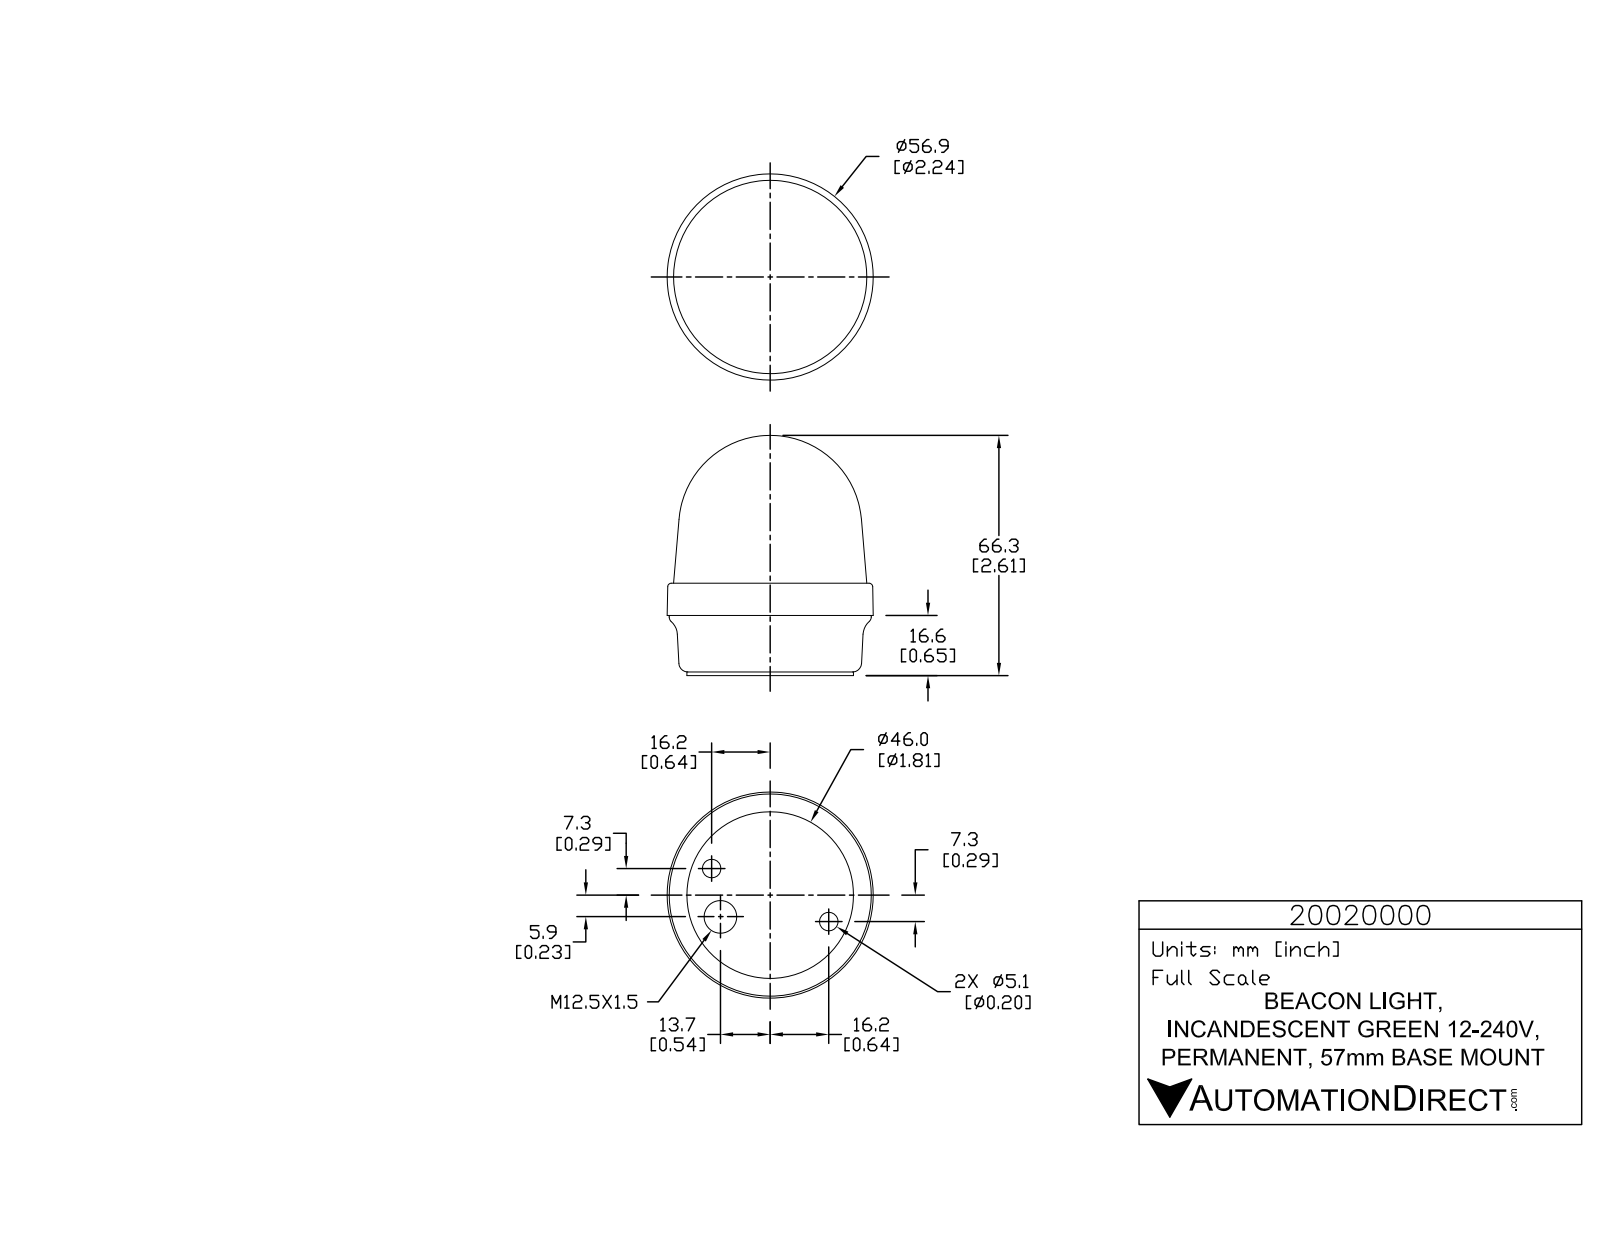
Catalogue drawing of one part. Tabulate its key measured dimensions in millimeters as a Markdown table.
| quantity | value |
| --- | --- |
| part name | 20020000 |
| STEP written by | SolidWorks 2015 (AUTOMOTIVE_DESIGN) |
| units | millimeters |
| bodies | 1 solid, 781 faces (526 planar, 163 cylindrical, 92 other) |
| overall size | 66.3 × 56.9 × 56.9 |
| volume | 123 400 mm³ |
| surface area | 13 350 mm² |
| round holes (diameter × count) | 1 × 3, 5.1 × 2, 9 × 1 |
| round bosses / shafts (diameter × count) | 5.7 × 3, 1.4 × 3, 55.8 × 1, 46 × 1 |
| partial cylindrical surfaces (radius × count) | 0.2 × 6, 0.2 × 6, 0.2 × 6, 3.3 × 6, 0.1 × 3, 0.1 × 3, 0.2 × 3, 0.2 × 3 |
| main face-to-face distances | 1, 16.6, 15.6, 25.5, 24.5, 8.9, 17.7, 34.3, 33.3, 8.8 |
| hole center spacings | 13.6, 29.9, 35.5 |
